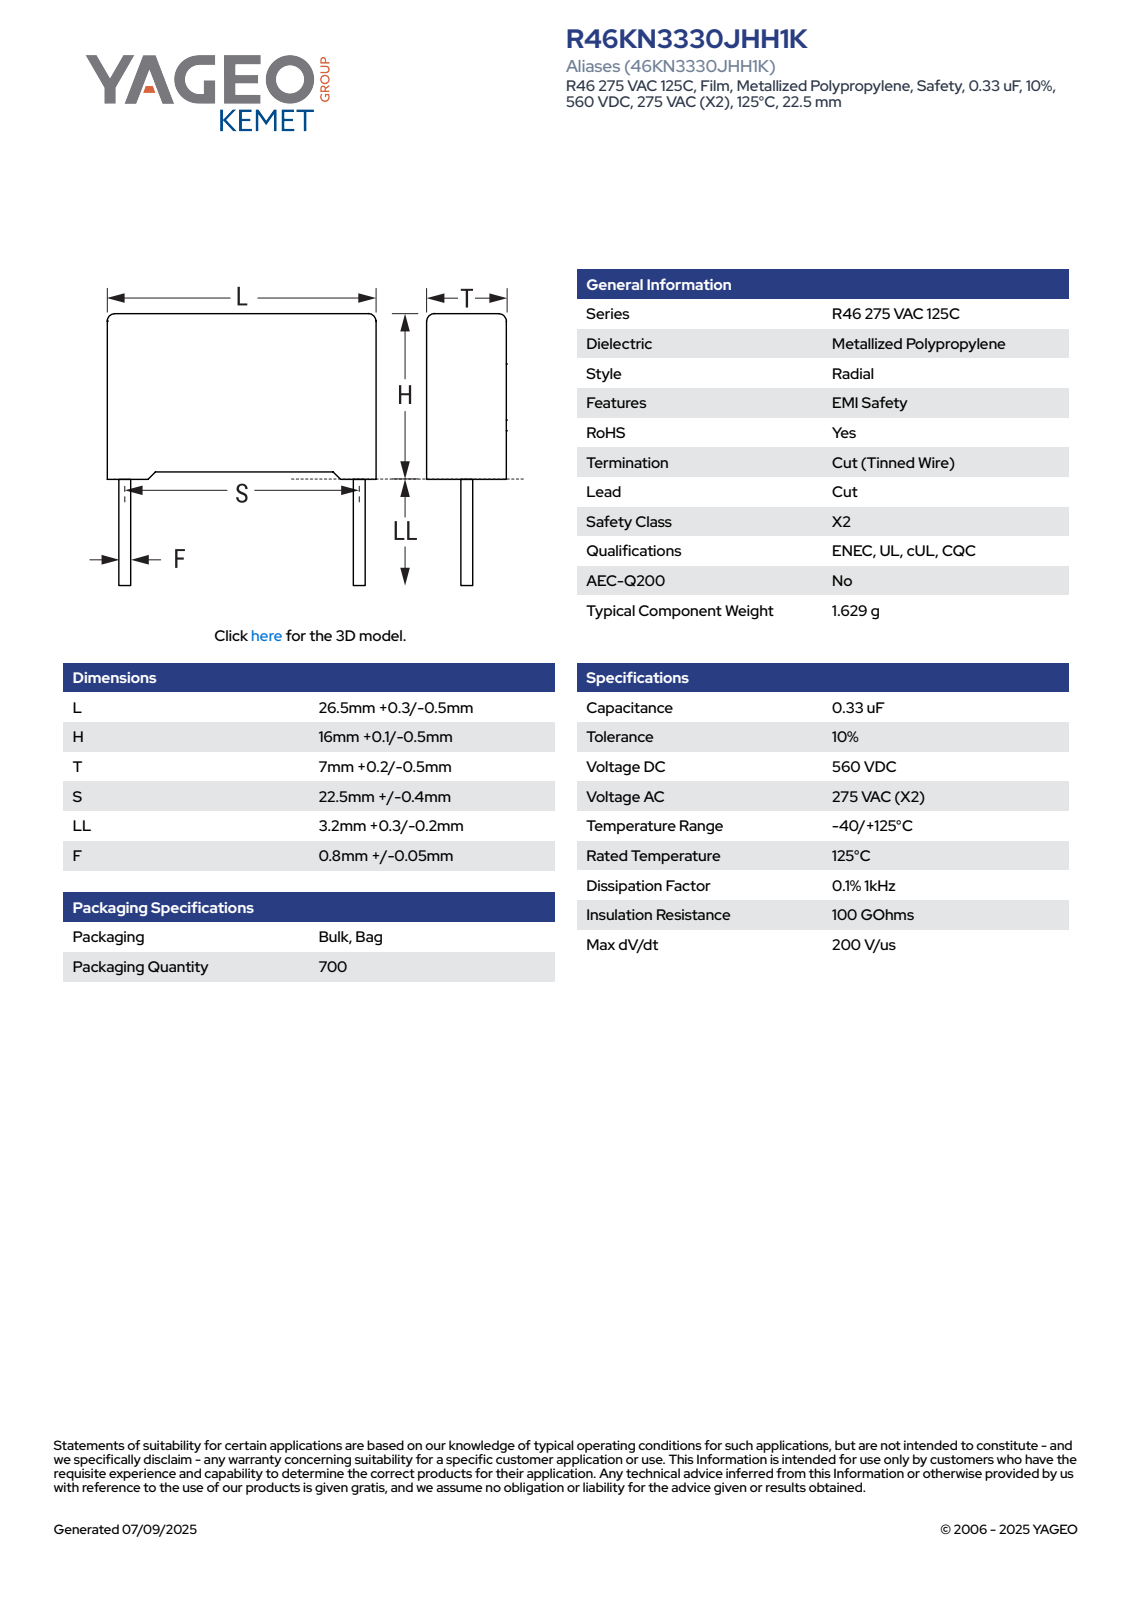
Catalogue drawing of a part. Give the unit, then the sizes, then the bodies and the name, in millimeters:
Units: millimetres
Overall size (bounding box): 26.8 × 19.6 × 7.21
Round bosses / shafts (diameter × count): ⌀0.85 ×2
Partial cylindrical surfaces — rounded edges, fillets, slot ends (radius × count): R0.5 ×4
Main face-to-face distances: 7.2, 15.35, 26.8, 15.54, 0.89, 0.56, 0.75, 16.1, 6.31, 5.42
Volume: 2 988 mm³ · Surface area: 1 547 mm²
Bodies: 4 solids, 85 faces (77 planar, 8 cylindrical, 0 other)
Part name (STEP PRODUCT): CFR_RB2_26.5X16X7_L26.8H16.1T7.2S22.5LL3.5F0.85
STEP written by: SolidWorks 2021 (AUTOMOTIVE_DESIGN)
